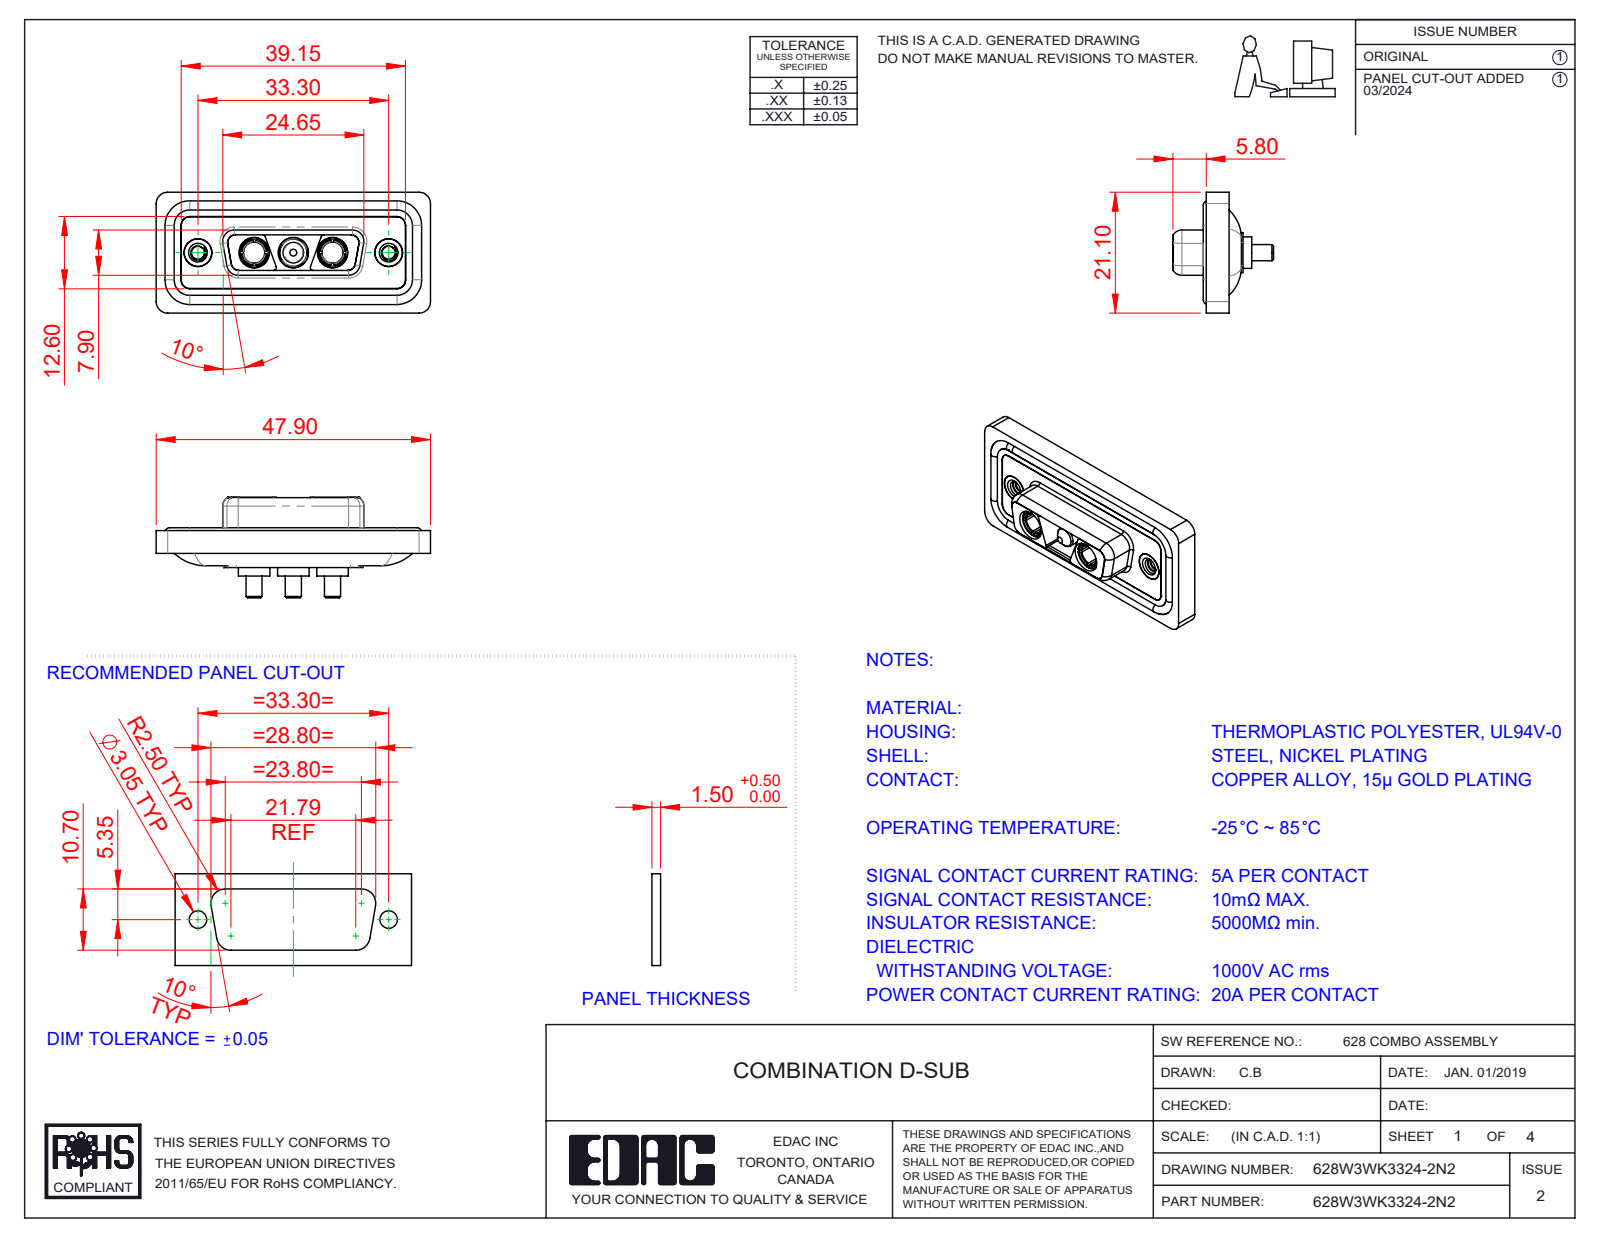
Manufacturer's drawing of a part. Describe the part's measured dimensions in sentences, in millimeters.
The part is named "Power Socket_20A S; 628Combo Waterproof Housing_15 Contacts; 628Combo Housing_3WK3; 628Combo Shell Front_15 Contacts (+4 more)". Its 3-D file was written by "SolidWorks 2023 (CONFIG_CONTROL_DESIGN)". It is 13 solids with 583 faces: 178 planar, 258 cylindrical and 147 other. Overall it measures 47.9 by 21.1 by 17.55 millimeters. Its volume is 5 878 cubic millimeters and its surface area 9 505 square millimeters. Round holes: 5 of diameter 4.85, 3 of diameter 5.3, 2 of diameter 2.26, 2 of diameter 3.7, 2 of diameter 4, 2 of diameter 4.05, 2 of diameter 5. Round bosses or shafts: 4 of diameter 1.6, 3 of diameter 5.5, 3 of diameter 5.2, 3 of diameter 4.75, 3 of diameter 3.75, 3 of diameter 2.8, 2 of diameter 4.96, 2 of diameter 4.95. Partial cylindrical surfaces (rounded edges, fillets, slot ends): 22 of radius 1.5, 20 of radius 2, 12 of radius 1.35, 8 of radius 0.5, 8 of radius 1.6, 4 of radius 0.25, 4 of radius 0.6, 4 of radius 0.65. The main face-to-face distances are 0.4, 1.6, 1.8, 0.5, 1.1, 2.9, 5.65, 7.05, 1.5, 5.35. The hole center spacings are 6.85, 9.8, 16.65, 23.5, 13.7, 33.3.
